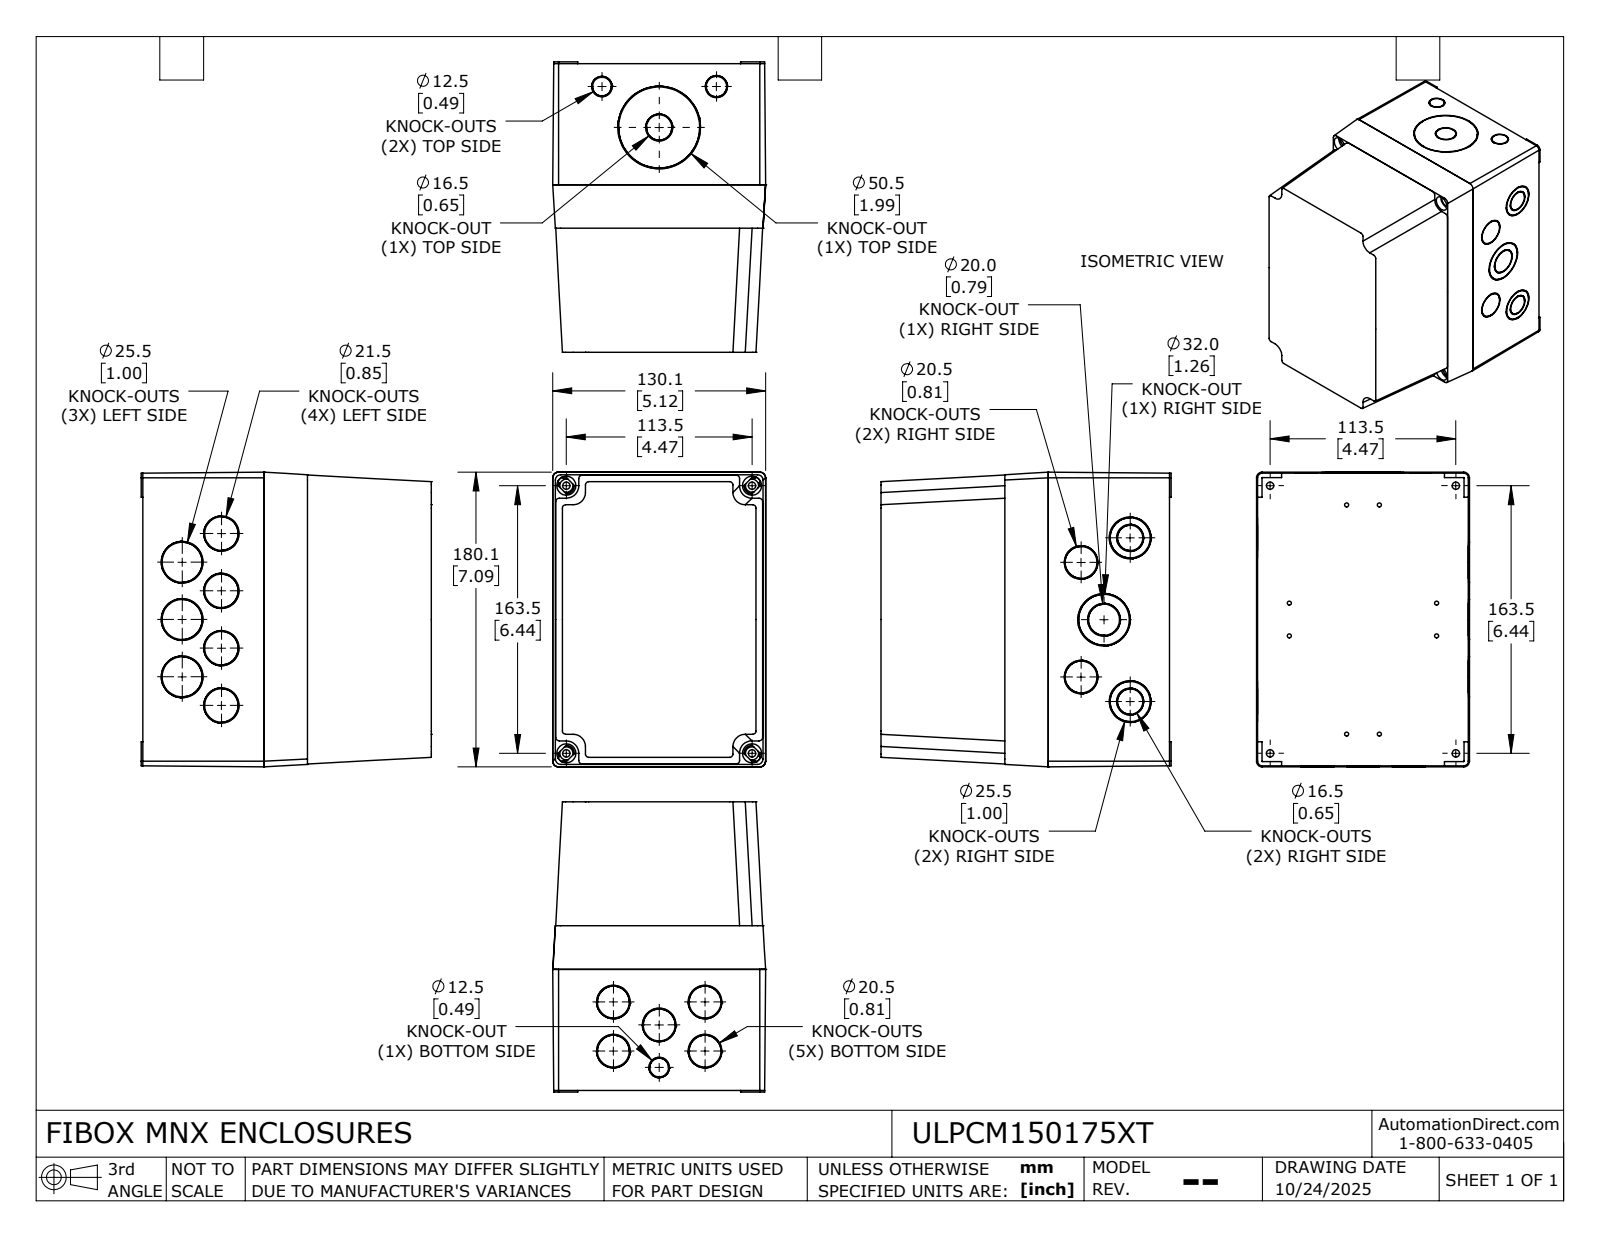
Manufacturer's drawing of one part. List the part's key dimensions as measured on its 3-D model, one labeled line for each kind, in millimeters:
Part name (STEP PRODUCT): ULPCM150175XT
STEP written by: SolidWorks 2024 (AUTOMOTIVE_DESIGN)
Units: millimetres
Bodies: 2 solids, 426 faces (212 planar, 184 cylindrical, 30 other)
Overall size (bounding box): 180.09 × 177.32 × 130.09
Volume: 709 343 mm³ · Surface area: 304 397 mm²
Round holes (diameter × count): ⌀2.5 ×8, ⌀3.2 ×8, ⌀20.5 ×7, ⌀25.5 ×5, ⌀4.5 ×4, ⌀8 ×4, ⌀11.59 ×4, ⌀21.5 ×4, ⌀12.5 ×1, ⌀13.5 ×1, ⌀16.5 ×1, ⌀20 ×1
Round bosses / shafts (diameter × count): ⌀8 ×8, ⌀19.5 ×7, ⌀24.5 ×5, ⌀20.5 ×4, ⌀15.5 ×3, ⌀11.5 ×2, ⌀49.5 ×1, ⌀31 ×1
Partial cylindrical surfaces — rounded edges, fillets, slot ends (radius × count): R2 ×12, R2.2 ×8, R1.21 ×6, R0.2 ×4, R2.85 ×4, R3.29 ×4, R3.49 ×4, R4.86 ×4
Main face-to-face distances: 4.22, 4.2, 172.12, 176.32, 3, 169.12, 173.32, 114.16, 164.15, 14.11
Hole centre spacings: 10, 29.7, 35, 90, 20, 33.85, 40, 40.31
